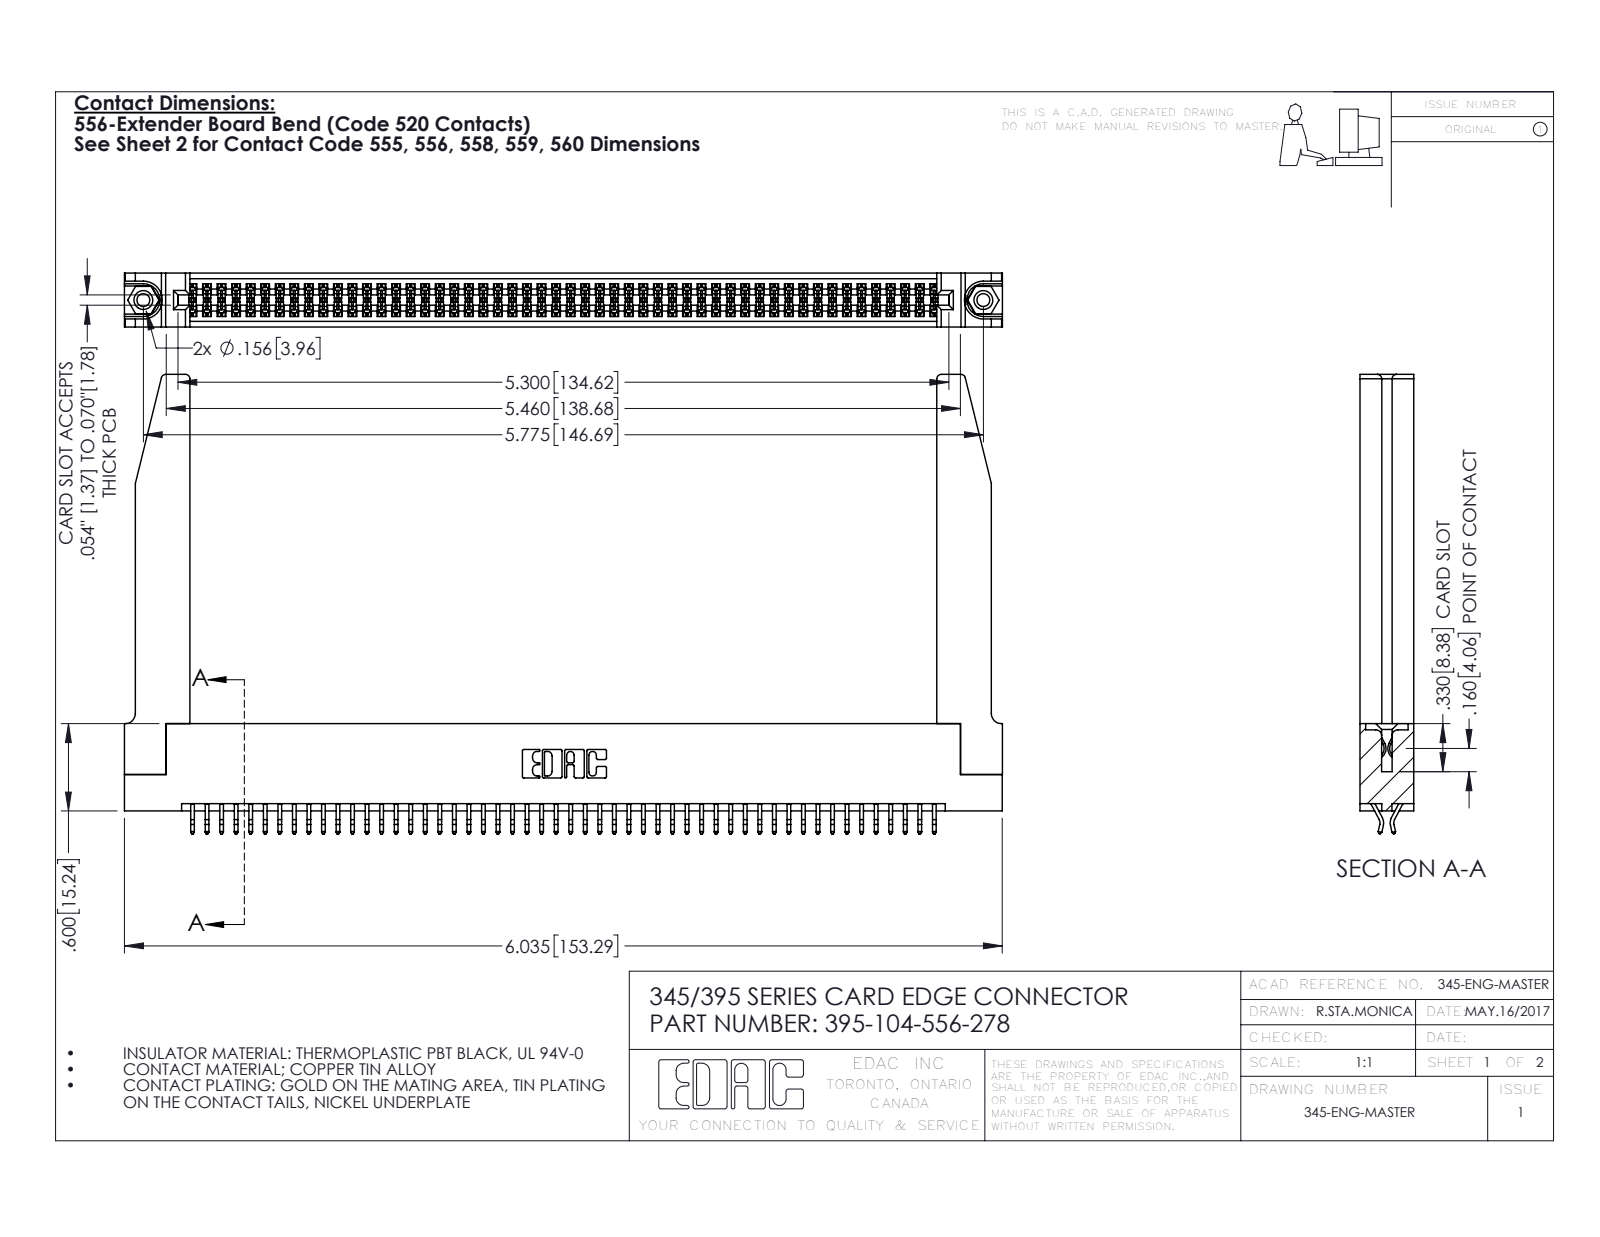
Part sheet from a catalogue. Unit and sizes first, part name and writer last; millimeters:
Units: millimetres
Overall size (bounding box): 153.3 × 80.2 × 9.4
Round holes (diameter × count): ⌀2.3 ×2, ⌀3.2 ×2, ⌀4 ×2, ⌀1.6 ×1
Round bosses / shafts (diameter × count): ⌀3.9 ×2
Partial cylindrical surfaces — rounded edges, fillets, slot ends (radius × count): R0.2 ×156, R0.3 ×22, R0.8 ×8, R0.2 ×6, R0.8 ×6, R0.7 ×3, R0.3 ×2, R0.4 ×2
Main face-to-face distances: 1.8, 9.4, 7.6, 5.1, 0.6, 2.5, 6.9, 5.7, 4.4, 3.8
Hole centre spacings: 6.9, 140.7, 146.7
Volume: 22 750 mm³ · Surface area: 29 080 mm²
Bodies: 109 solids, 6184 faces (4070 planar, 2062 cylindrical, 52 other)
Part name (STEP PRODUCT): 345-220-078_345-220-078; 345-250-001_345-250-001-102; 345 Part_Flush Mounting Lugs - 0.156 Dia-TH; 395-104-556-278 (+1 more)
STEP written by: SolidWorks 2016 (CONFIG_CONTROL_DESIGN)
